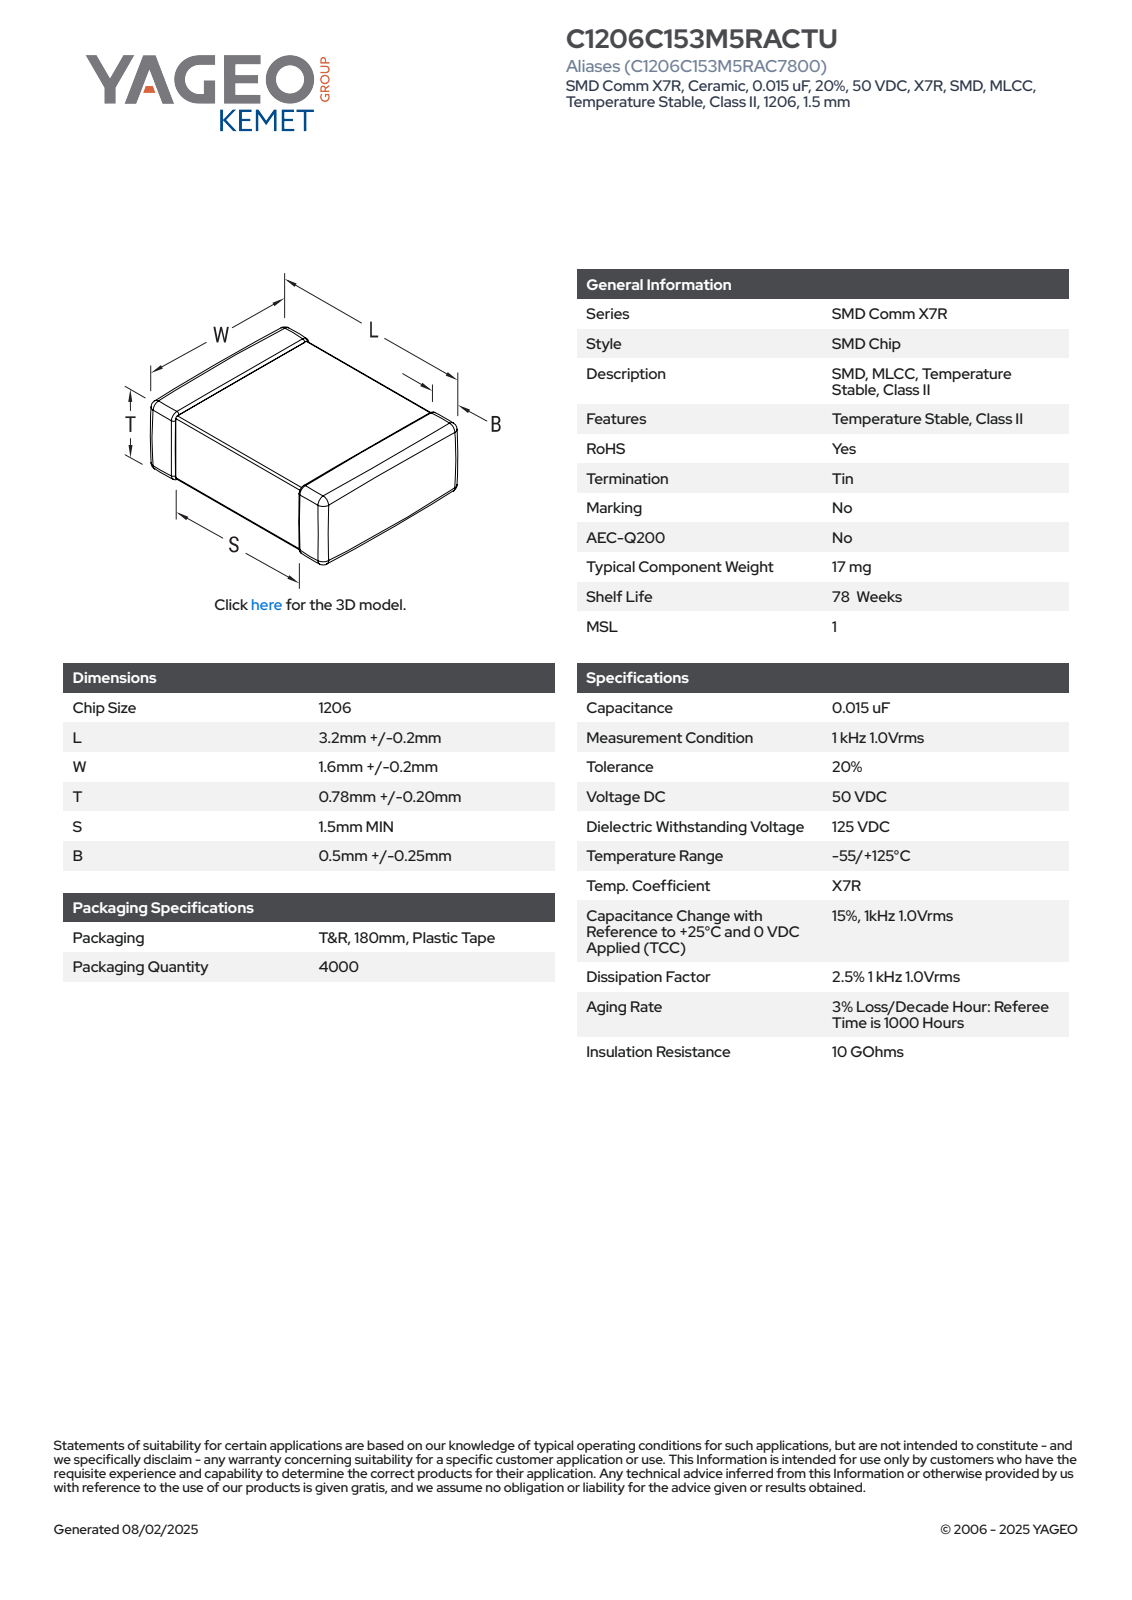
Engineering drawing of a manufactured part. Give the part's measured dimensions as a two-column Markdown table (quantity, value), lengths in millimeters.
| quantity | value |
| --- | --- |
| part name | CCS_CCSTD_1206_L3.4W1.8T0.98B0.5 |
| STEP written by | SolidWorks 2021 (AUTOMOTIVE_DESIGN) |
| units | millimeters |
| bodies | 4 solids, 125 faces (71 planar, 38 cylindrical, 16 other) |
| overall size | 3.4 × 1.8 × 0.98 |
| volume | 6 mm³ |
| surface area | 22 mm² |
| main face-to-face distances | 0.94, 0.9, 1.76, 0.98, 1.72, 3.4, 1.8, 0.95, 0.91, 1.57 |
